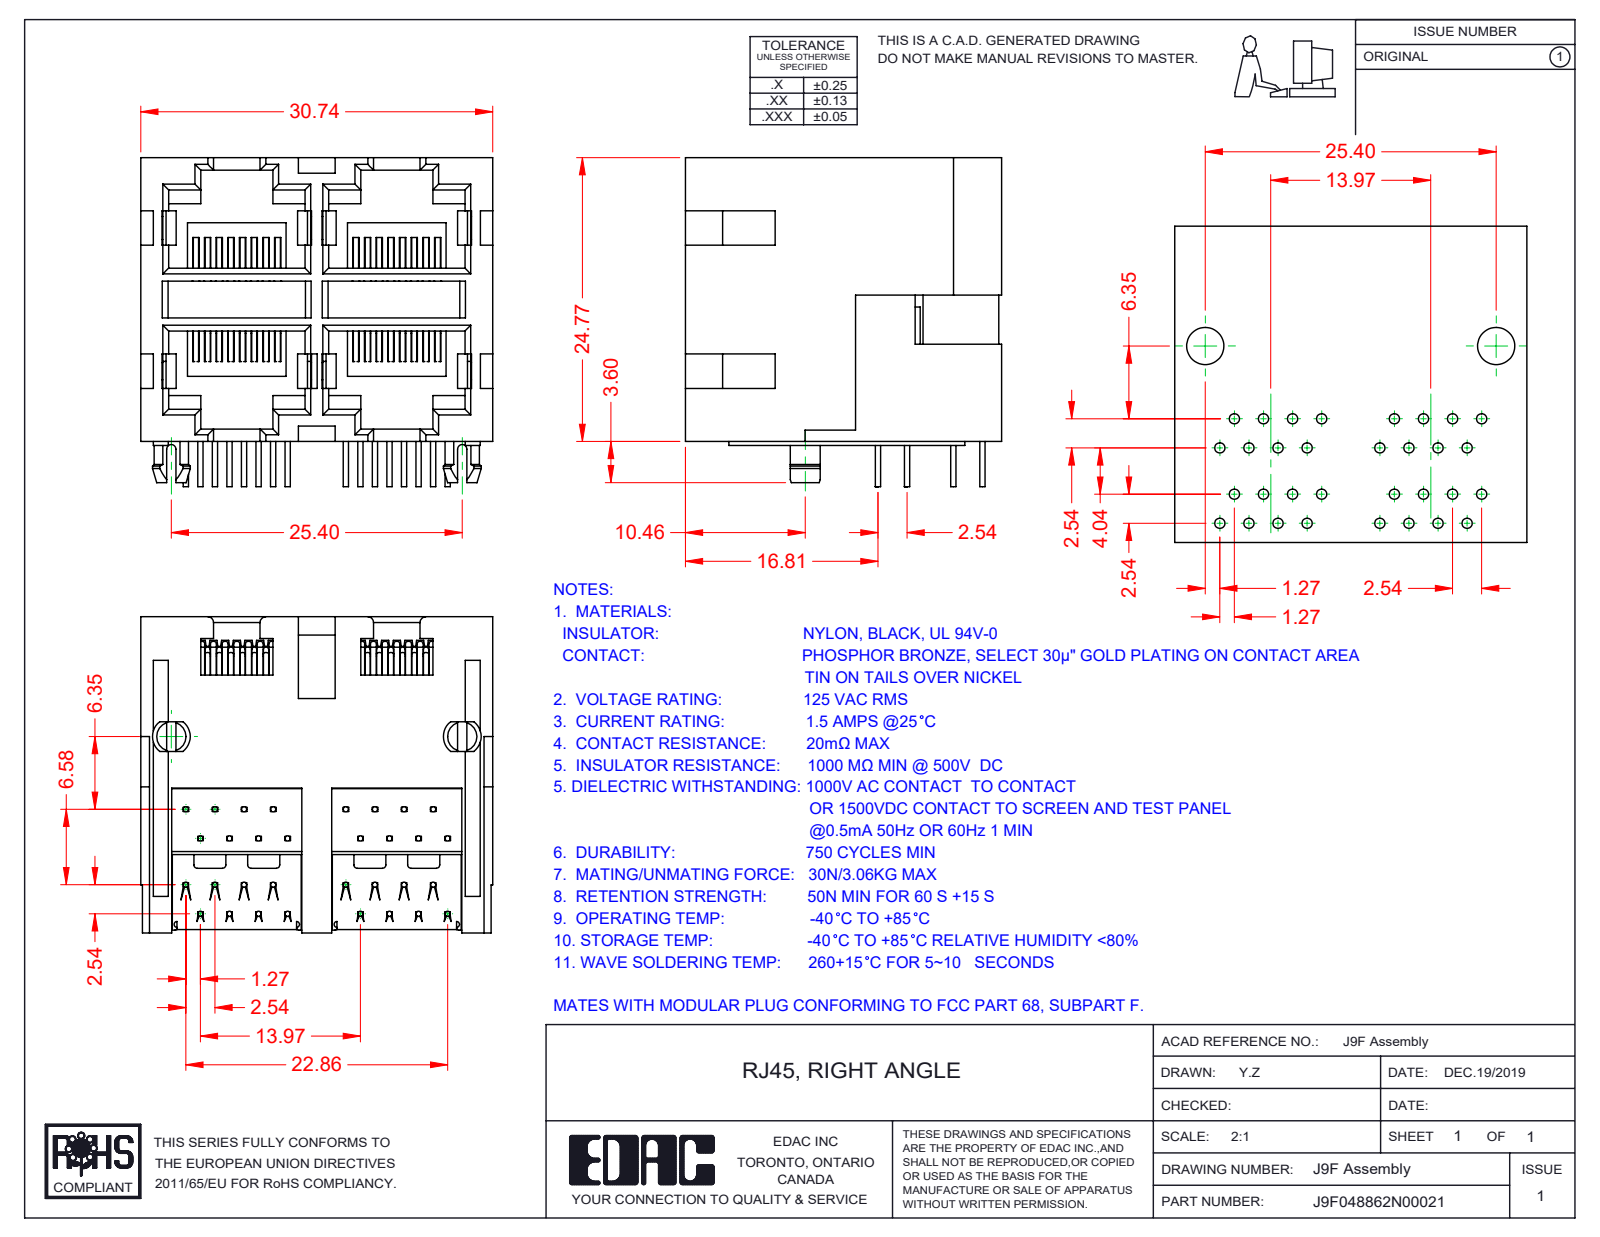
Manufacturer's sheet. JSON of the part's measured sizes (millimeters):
{"part_name": "9F Contact Lock Lower; RJ9F048862N00021; 9F Contacts Upper; 9F Insulator (+2 more)", "step_written_by": "SolidWorks 2016 (CONFIG_CONTROL_DESIGN)", "units": "millimeters", "bodies": {"solids": 37, "faces": 2810, "planar": 1899, "cylindrical": 557, "other": 354}, "overall_size": [30.74, 28.71, 27.6], "volume_mm3": 11763, "surface_area_mm2": 19774, "round_bosses_or_shafts": [[0.46, 144]], "partial_cylinders_radius": [[0.2, 63], [0.5, 25], [0.3, 9], [0.25, 4], [0.4, 2], [0.45, 2], [1.5, 2], [1.65, 2]], "face_to_face_distances": [13.97, 1, 0.35, 12.7, 15, 13.05, 11.98, 1.05, 13.62, 5.5]}
